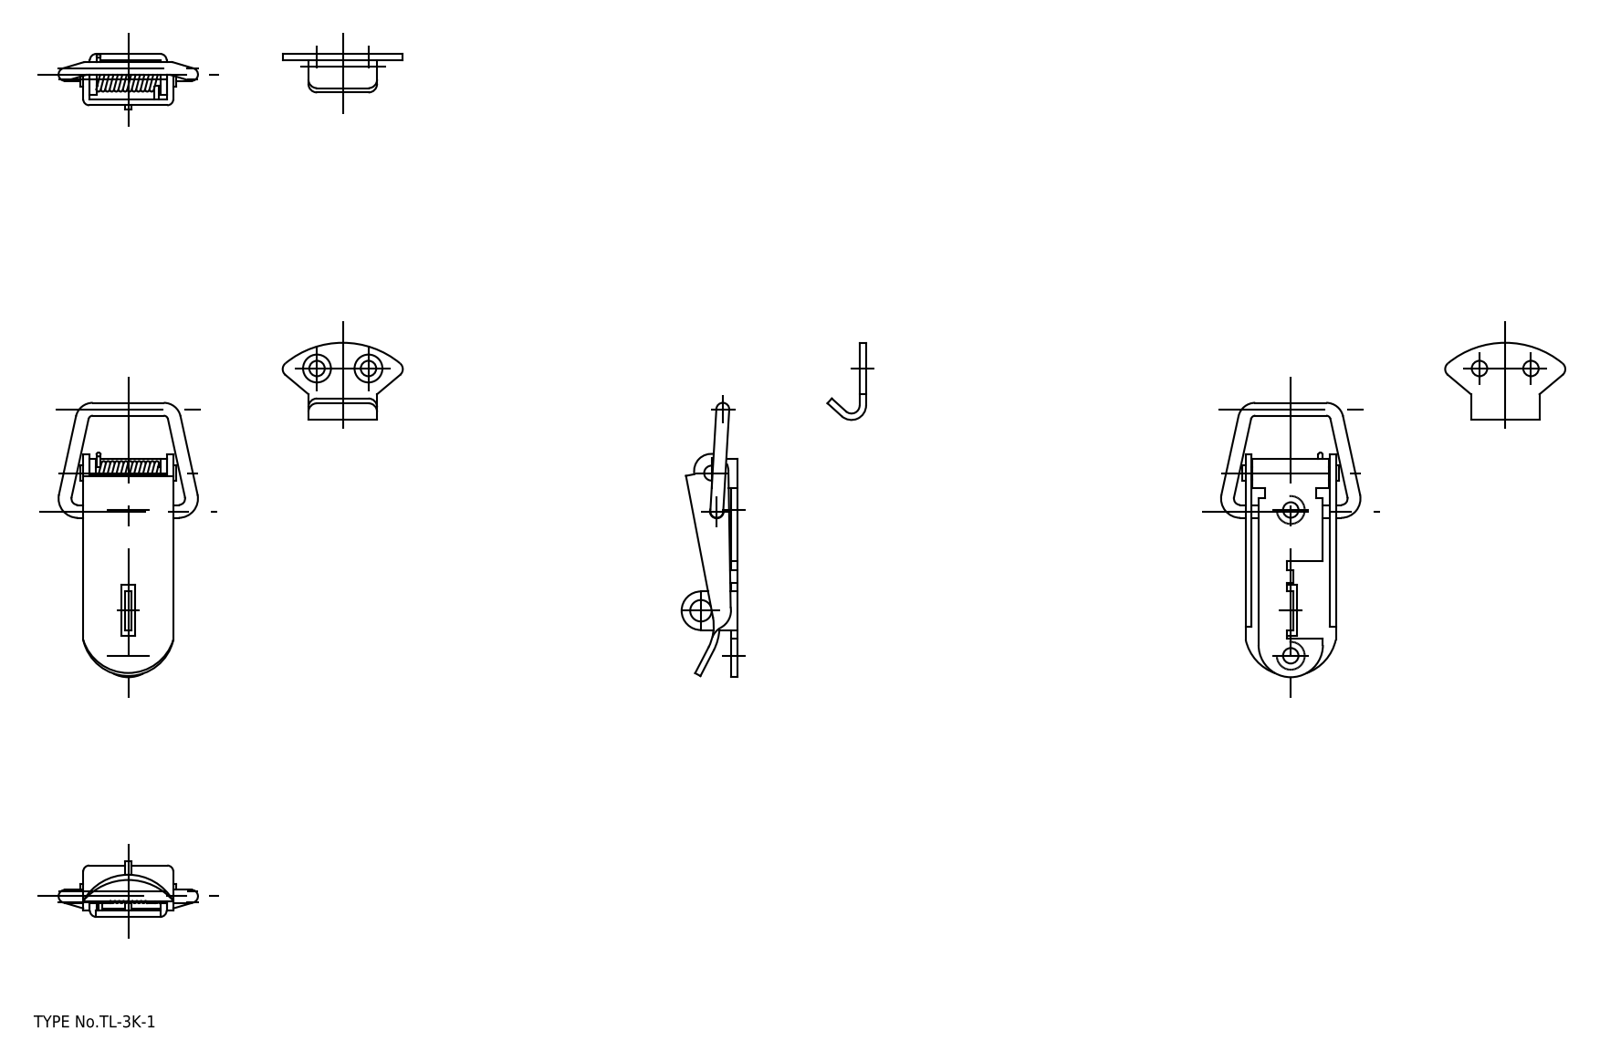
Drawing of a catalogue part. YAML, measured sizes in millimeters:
part_name: "spring; lever; base; shaft (+2 more)"
step_written_by: "spGate 17.5.2 (AUTOMOTIVE_DESIGN)"
units: millimeters
bodies: {solids: 6, faces: 173, planar: 67, cylindrical: 60, other: 46}
overall_size: [78.5, 32.5, 13.01]
volume: 4687
surface_area: 7730
round_holes:
  - {diameter: 3.6, count: 4}
  - {diameter: 3.1, count: 1}
  - {diameter: 3.2, count: 1}
  - {diameter: 5, count: 1}
round_bosses_or_shafts:
  - {diameter: 3, count: 5}
partial_cylinders:
  - {radius: 1.5, count: 5}
  - {radius: 4.5, count: 3}
  - {radius: 1.75, count: 2}
  - {radius: 2, count: 2}
  - {radius: 3.4, count: 2}
  - {radius: 1.9, count: 1}
  - {radius: 4, count: 1}
  - {radius: 7.5, count: 1}
face_to_face_distances: [1.5, 19.5, 18, 1.4, 9.8, 21, 9.7, 1.55, 17.95, 16.45]
hole_center_spacings: [34.03, 67.77, 9.01, 12, 23.42, 32.2, 34]
